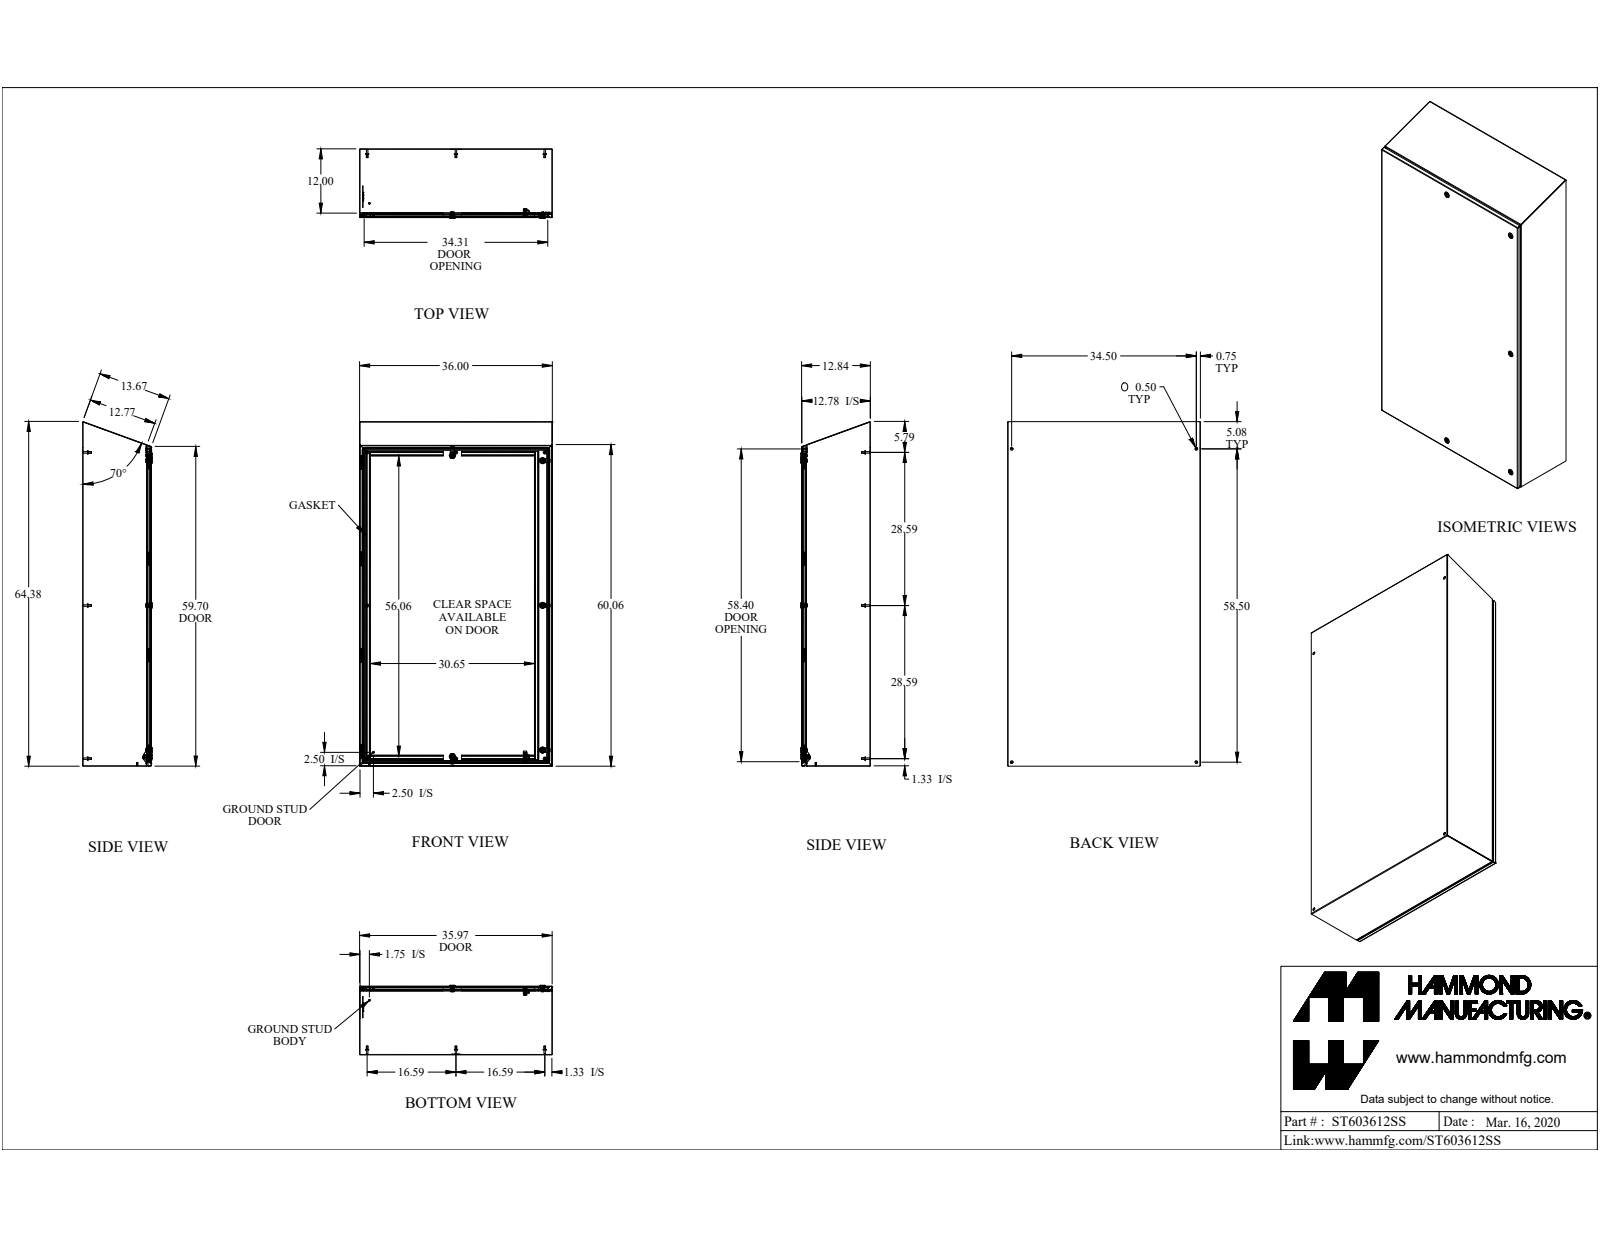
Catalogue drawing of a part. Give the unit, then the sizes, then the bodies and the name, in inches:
Units: inches
Overall size (bounding box): 64.334 × 36 × 12.997
Round holes (diameter × count): ⌀0.5 ×9, ⌀0.197 ×5, ⌀0.387 ×5, ⌀0.63 ×5, ⌀0.768 ×5, ⌀0.172 ×1, ⌀0.196 ×1, ⌀0.24 ×1, ⌀0.242 ×1, ⌀0.275 ×1, ⌀0.375 ×1
Round bosses / shafts (diameter × count): ⌀0.313 ×10, ⌀0.625 ×9, ⌀0.275 ×8, ⌀1.1 ×5, ⌀0.625 ×5, ⌀0.236 ×5, ⌀0.785 ×3, ⌀0.525 ×3
Partial cylindrical surfaces — rounded edges, fillets, slot ends (radius × count): R0.043 ×24, R0.036 ×19, R0.108 ×18, R0.062 ×17, R0.125 ×12, R0.094 ×10, R0.04 ×9, R0.006 ×8
Main face-to-face distances: 0.072, 12.693, 12.765, 0.072, 12.765, 12.837, 35.928, 35.856, 36, 0.04
Hole centre spacings: 34.5, 58.5, 67.915, 2.439, 2.494, 3.543, 4.444, 13.564
Volume: 561.2 in³ · Surface area: 15 928 in²
Bodies: 67 solids, 1483 faces (914 planar, 400 cylindrical, 169 other)
Part name (STEP PRODUCT): ST603612SS
STEP written by: SolidWorks 2019 (AUTOMOTIVE_DESIGN)
